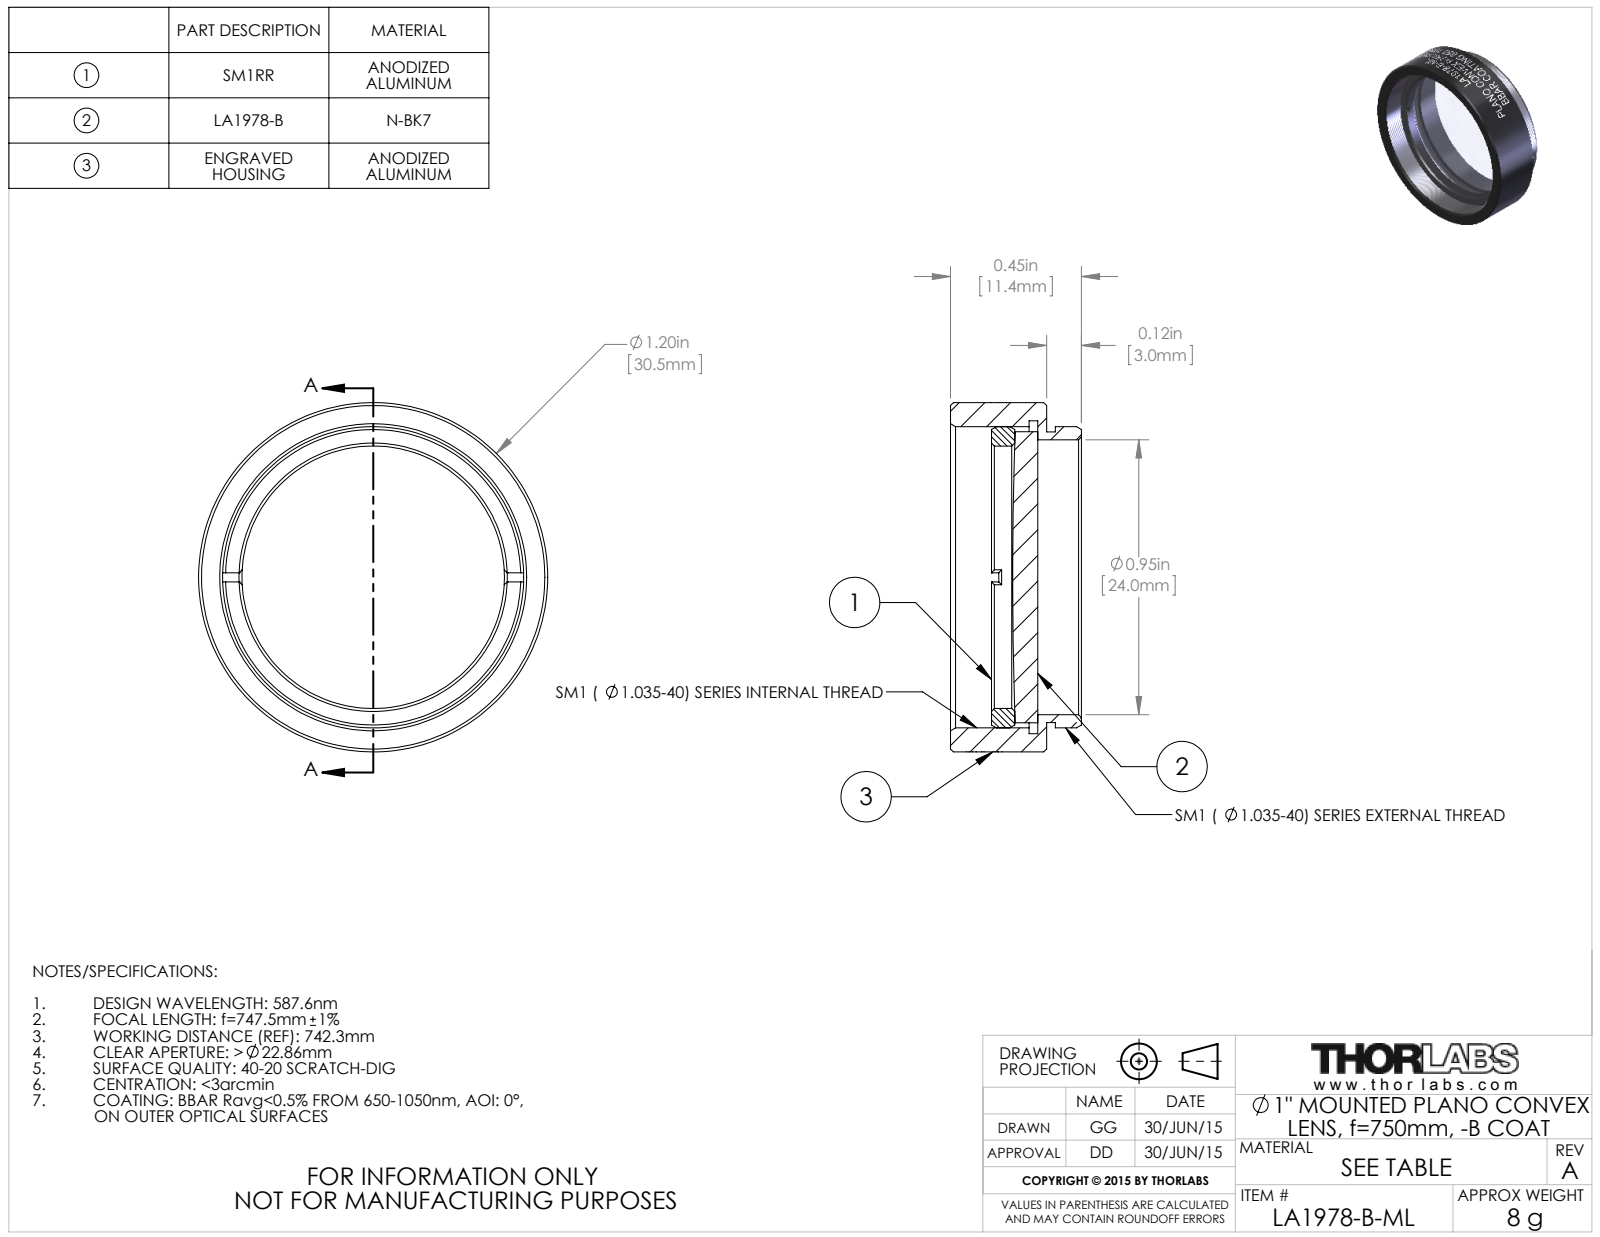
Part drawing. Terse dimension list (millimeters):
name: TTN039660-E0W
written by: SolidWorks 2014 (CONFIG_CONTROL_DESIGN)
unit: mm
bodies: 3 solids, 156 faces (20 planar, 112 cylindrical, 24 other)
size: 30.5 × 30.5 × 11.4
volume: 3 150 mm³; area: 4 312 mm²
holes: 1× ⌀22.9, 1× ⌀24, 1× ⌀27.3
bosses: 1× ⌀30.5, 1× ⌀26.3, 1× ⌀25.4, 1× ⌀25.4
face distances: 0.8, 8.4, 7.6, 2.8, 2, 5.6, 4.8, 4, 2, 3.6
